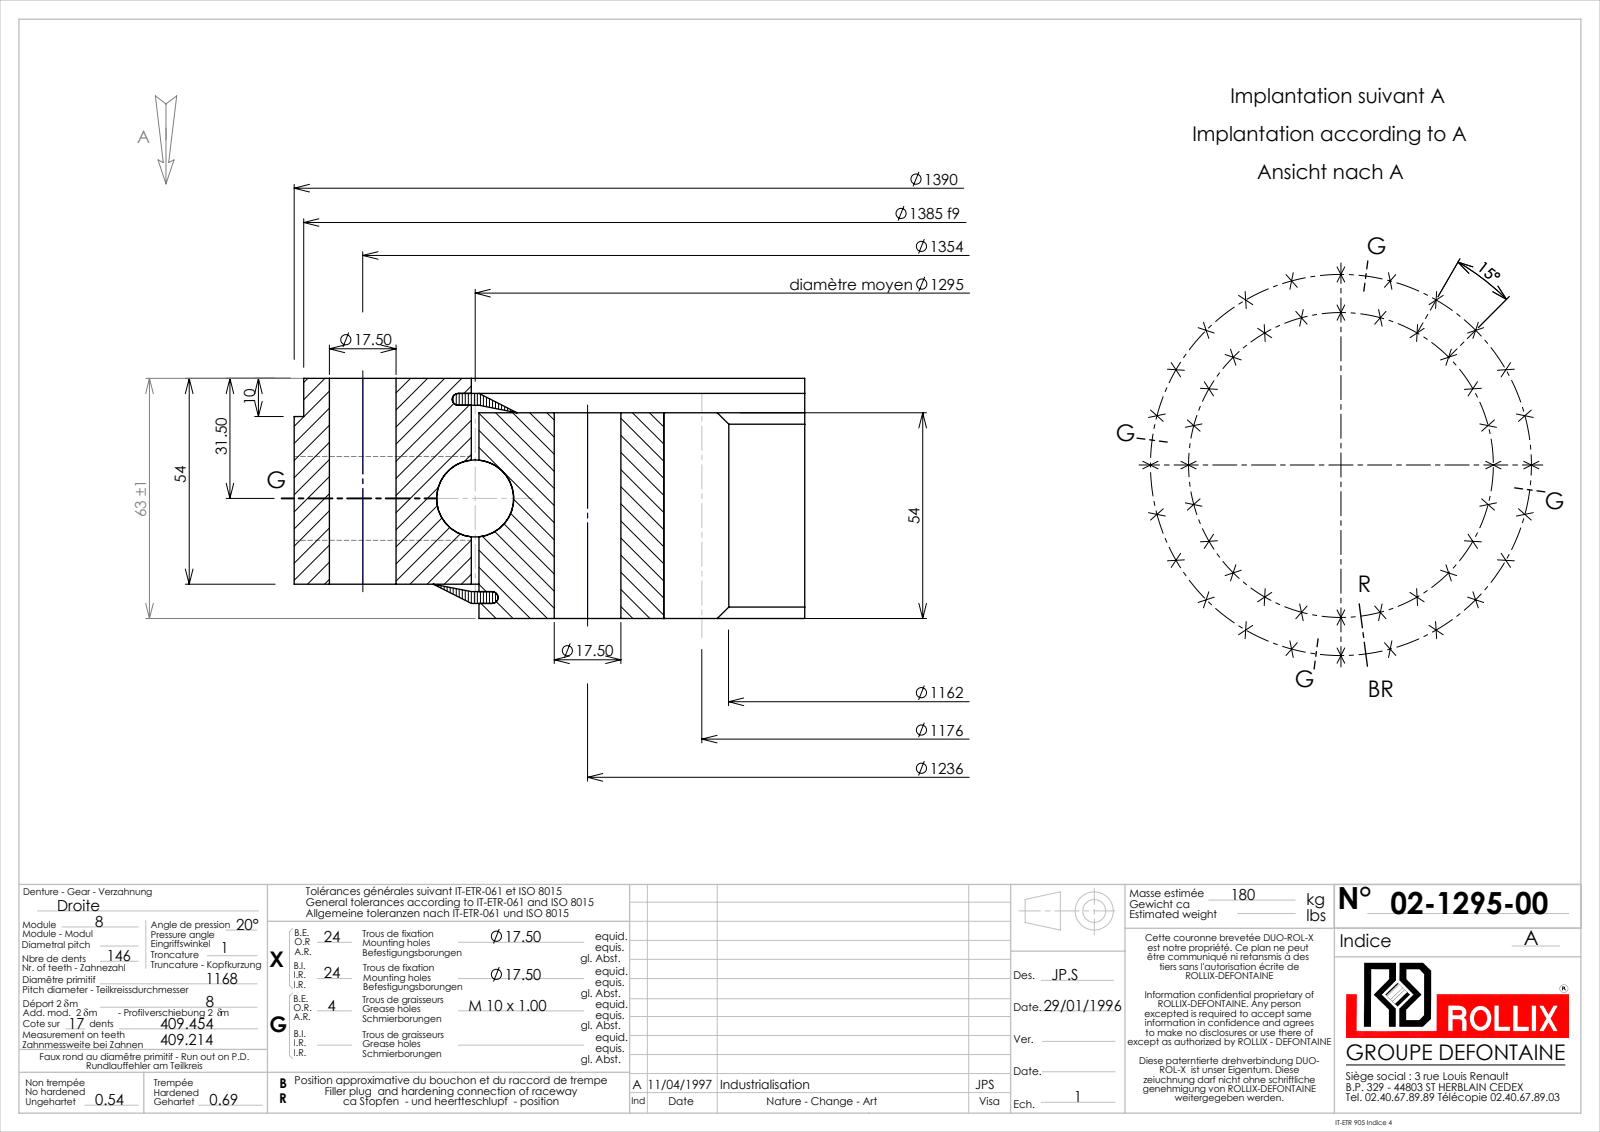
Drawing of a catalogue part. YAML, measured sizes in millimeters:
part_name: "02-1295-00"
step_written_by: "SolidWorks 2016 (CONFIG_CONTROL_DESIGN)"
units: millimeters
bodies: {solids: 5, faces: 1038, planar: 305, cylindrical: 413, other: 320}
overall_size: [1390, 1390, 63]
volume: 20970000
surface_area: 2470000
round_holes:
  - {diameter: 17.5, count: 48}
  - {diameter: 9, count: 4}
  - {diameter: 1297.03, count: 1}
round_bosses_or_shafts:
  - {diameter: 1390, count: 1}
  - {diameter: 1385, count: 1}
  - {diameter: 1292.98, count: 1}
partial_cylinders:
  - {radius: 581, count: 1}
  - {radius: 598, count: 1}
face_to_face_distances: [54, 9, 45, 63, 7.05, 55.95, 1.95, 46.95, 3.95, 59.05]
hole_center_spacings: [161.33, 319.9, 618, 873.98, 980.58, 1141.91, 1193.88, 1225.42]
